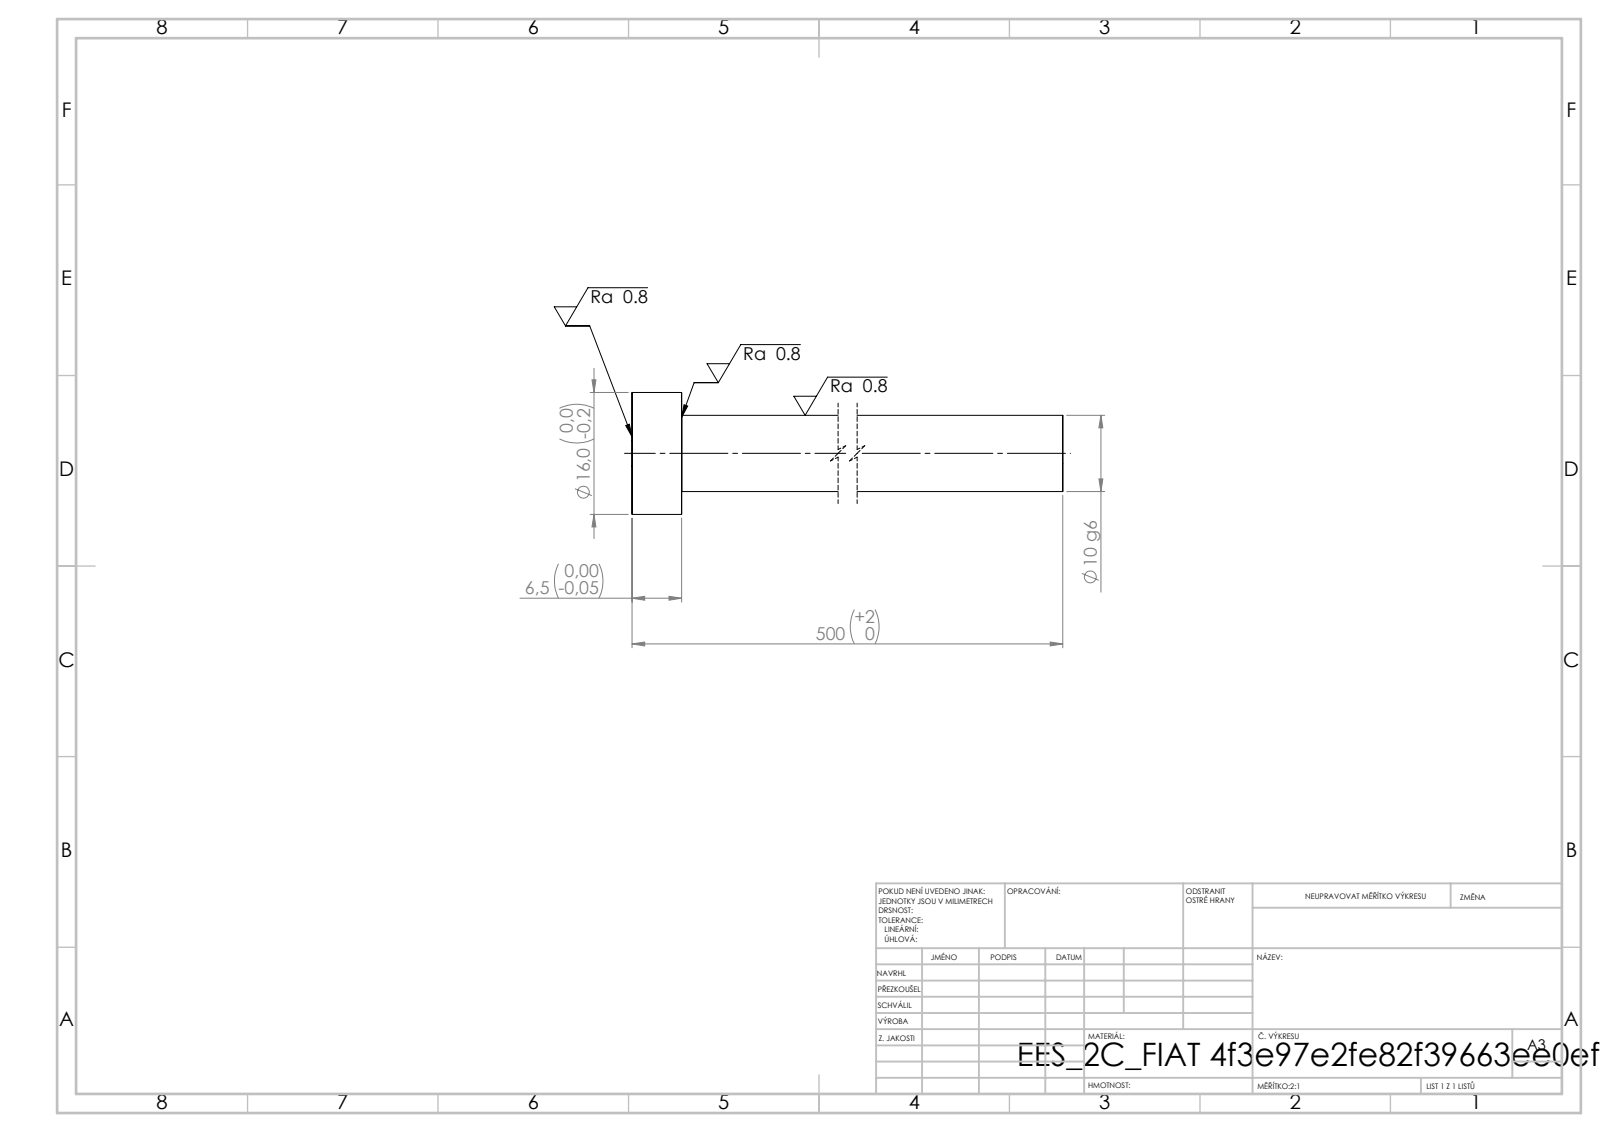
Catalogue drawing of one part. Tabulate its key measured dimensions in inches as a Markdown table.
| quantity | value |
| --- | --- |
| STEP written by | SolidWorks 2019 (CONFIG_CONTROL_DESIGN) |
| units | inches |
| bodies | 1 solid, 7 faces (3 planar, 4 cylindrical, 0 other) |
| overall size | 19.685 × 0.63 × 0.63 |
| volume | 2.445 in³ |
| surface area | 25.16 in² |
| round bosses / shafts (diameter × count) | 0.63 × 1, 0.394 × 1 |
| main face-to-face distances | 0.256, 19.685, 19.429 |
